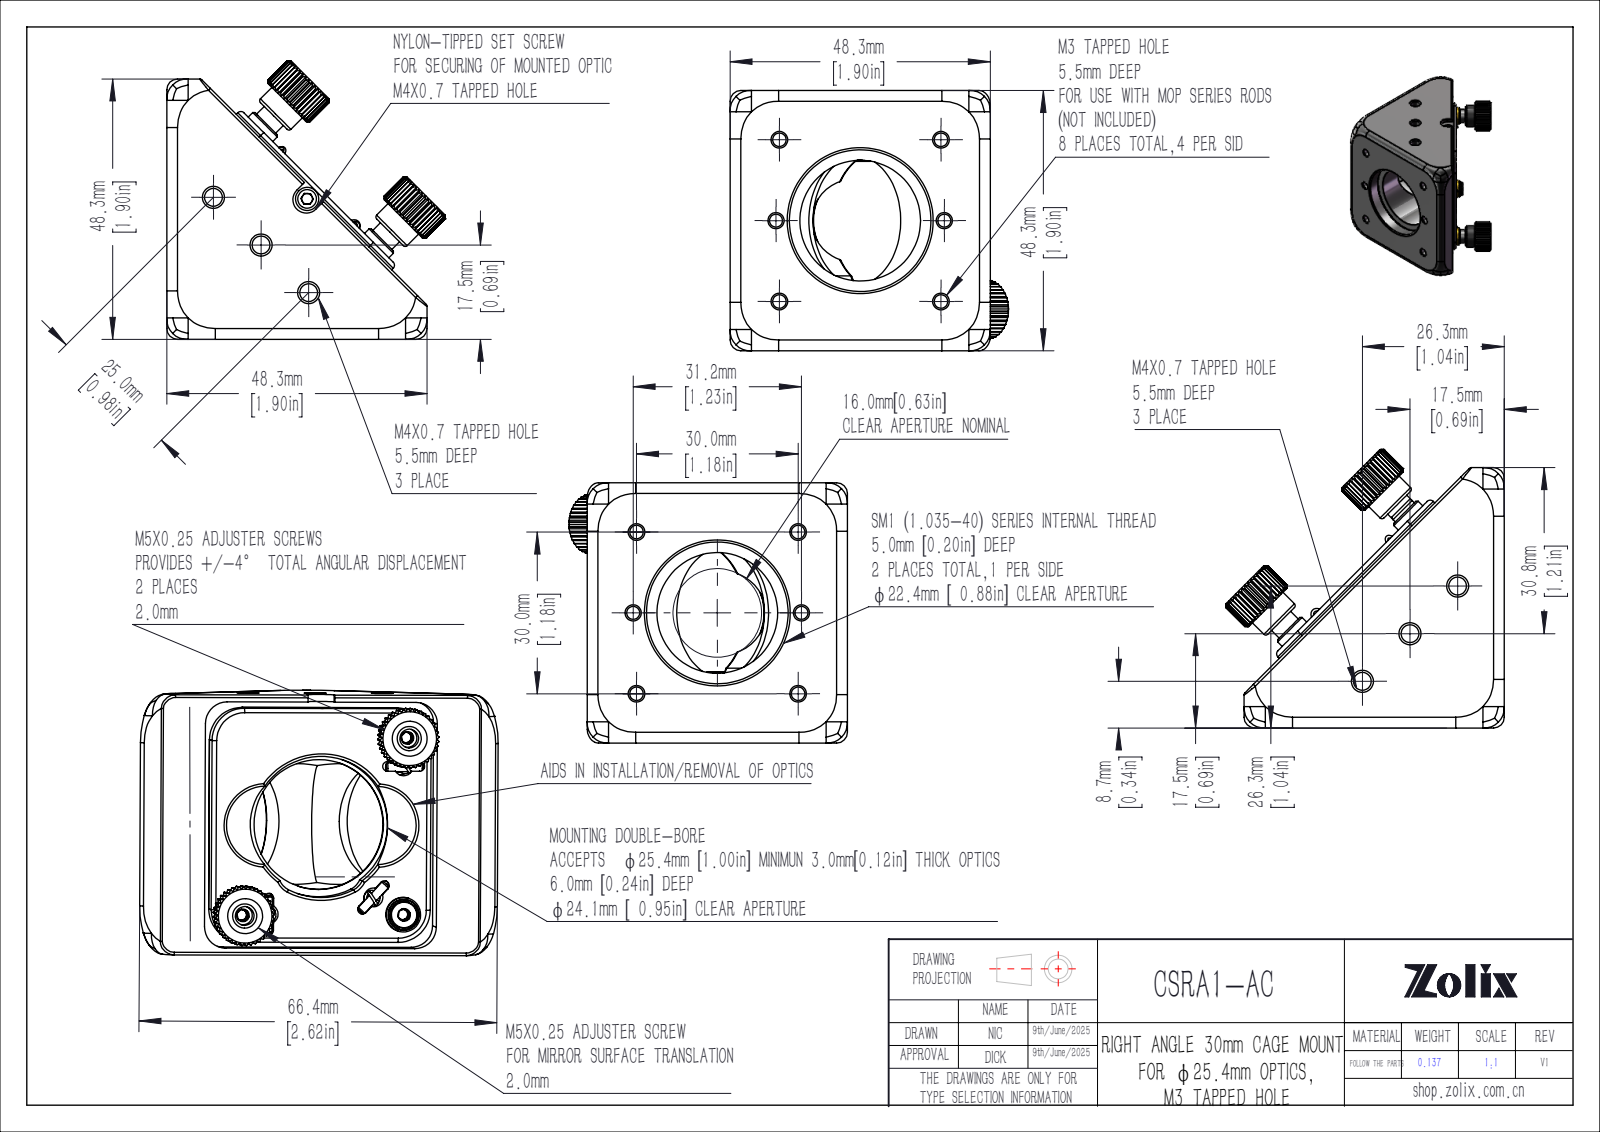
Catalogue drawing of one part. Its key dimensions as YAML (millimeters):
part_name: "CSRA1-AC"
step_written_by: "SolidWorks 2020 (CONFIG_CONTROL_DESIGN)"
units: millimeters
bodies: {solids: 20, faces: 1137, planar: 519, cylindrical: 273, other: 345}
overall_size: [51.69, 51.69, 48.3]
volume: 47751
surface_area: 22580
round_holes:
  - {diameter: 2.5, count: 9}
  - {diameter: 3.5, count: 5}
  - {diameter: 3.3, count: 4}
  - {diameter: 1.95, count: 3}
  - {diameter: 2.05, count: 3}
  - {diameter: 5, count: 3}
  - {diameter: 6.4, count: 3}
  - {diameter: 2.4, count: 2}
  - {diameter: 2.41, count: 2}
  - {diameter: 22.4, count: 2}
  - {diameter: 26.29, count: 2}
  - {diameter: 27.3, count: 2}
round_bosses_or_shafts:
  - {diameter: 7.1, count: 3}
  - {diameter: 1.6, count: 3}
  - {diameter: 8, count: 2}
  - {diameter: 6, count: 2}
  - {diameter: 4, count: 1}
  - {diameter: 2.5, count: 1}
partial_cylinders:
  - {radius: 0.8, count: 8}
  - {radius: 2, count: 7}
  - {radius: 0.9, count: 6}
  - {radius: 0.3, count: 4}
  - {radius: 0.5, count: 4}
  - {radius: 4, count: 4}
  - {radius: 6, count: 4}
  - {radius: 3.65, count: 3}
face_to_face_distances: [48.3, 1.2, 2.5, 8.39, 5.89, 9.59, 7.09, 1.3, 47, 5]
hole_center_spacings: [15.01, 21.21, 30, 34.1, 15.62, 42.43, 5.5, 12.5]
